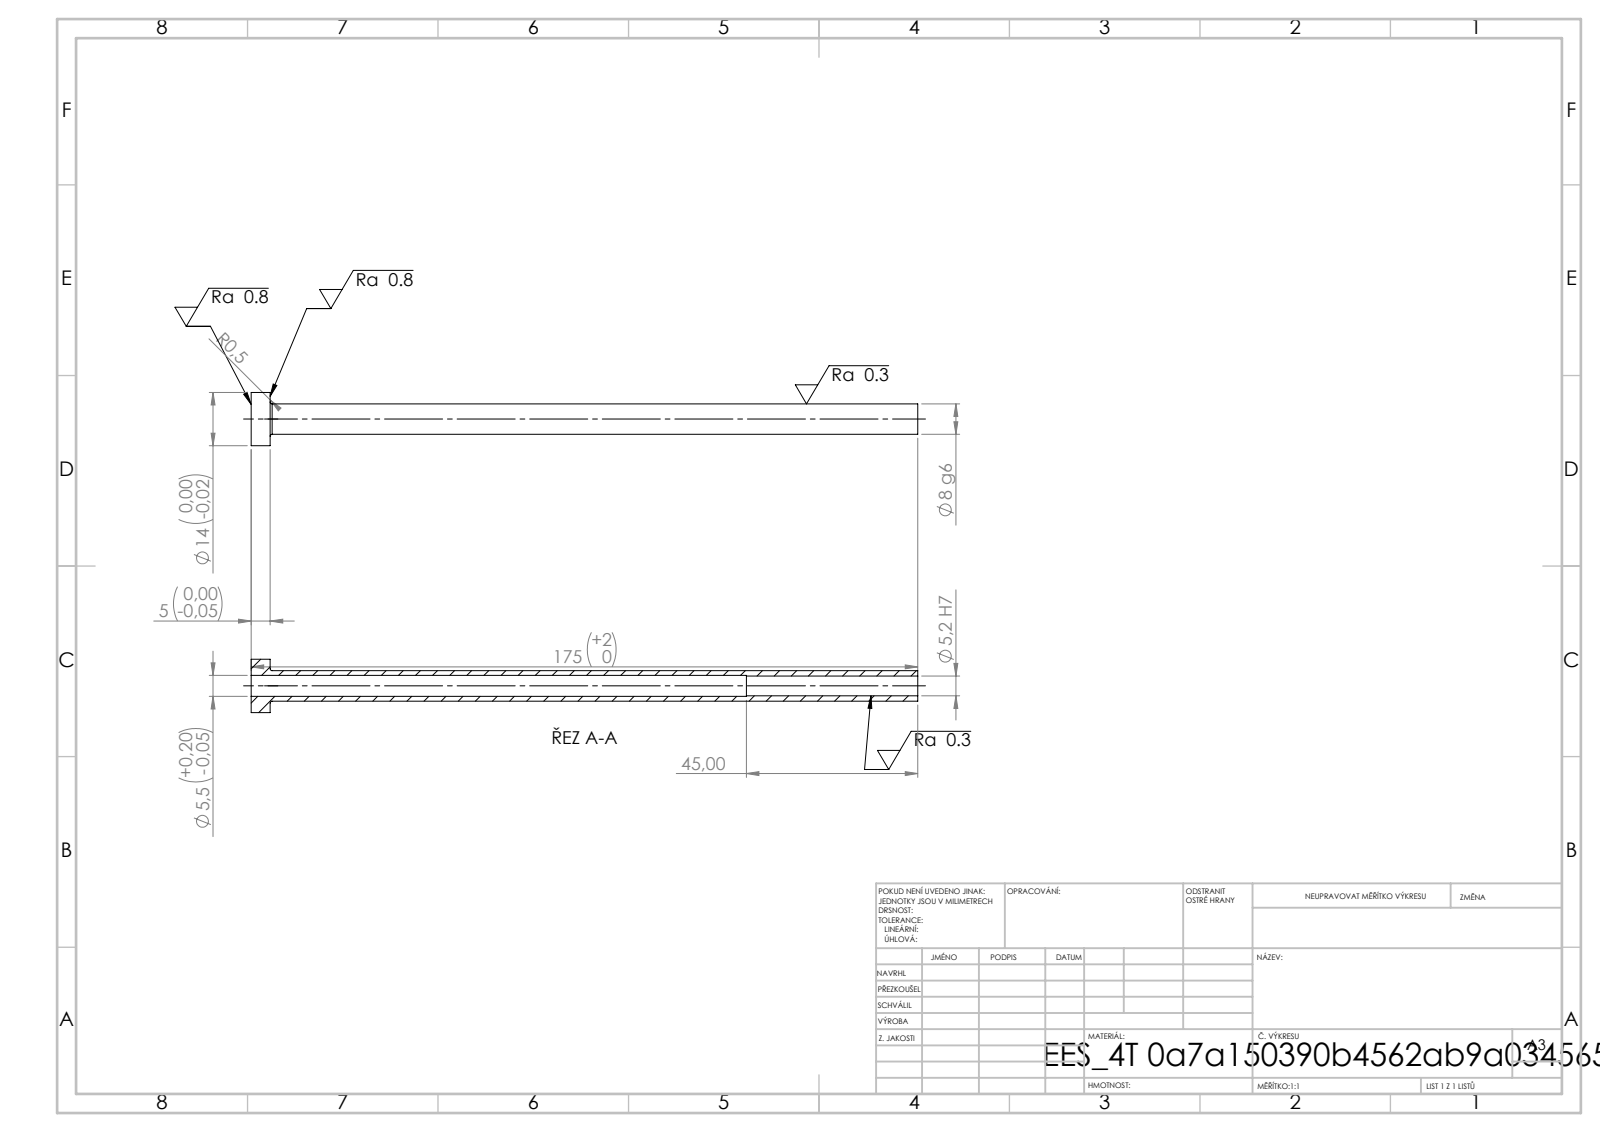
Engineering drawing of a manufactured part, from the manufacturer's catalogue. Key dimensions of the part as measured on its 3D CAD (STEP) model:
STEP written by: SolidWorks 2019 (CONFIG_CONTROL_DESIGN)
Units: millimetres
Bodies: 1 solid, 14 faces (4 planar, 8 cylindrical, 2 other)
Overall size (bounding box): 175 × 14 × 14
Volume: 5 272 mm³ · Surface area: 7 734 mm²
Round holes (diameter × count): ⌀5.2 ×1, ⌀5.5 ×1
Round bosses / shafts (diameter × count): ⌀14 ×1, ⌀8 ×1
Main face-to-face distances: 5, 175, 170, 130, 125, 45
